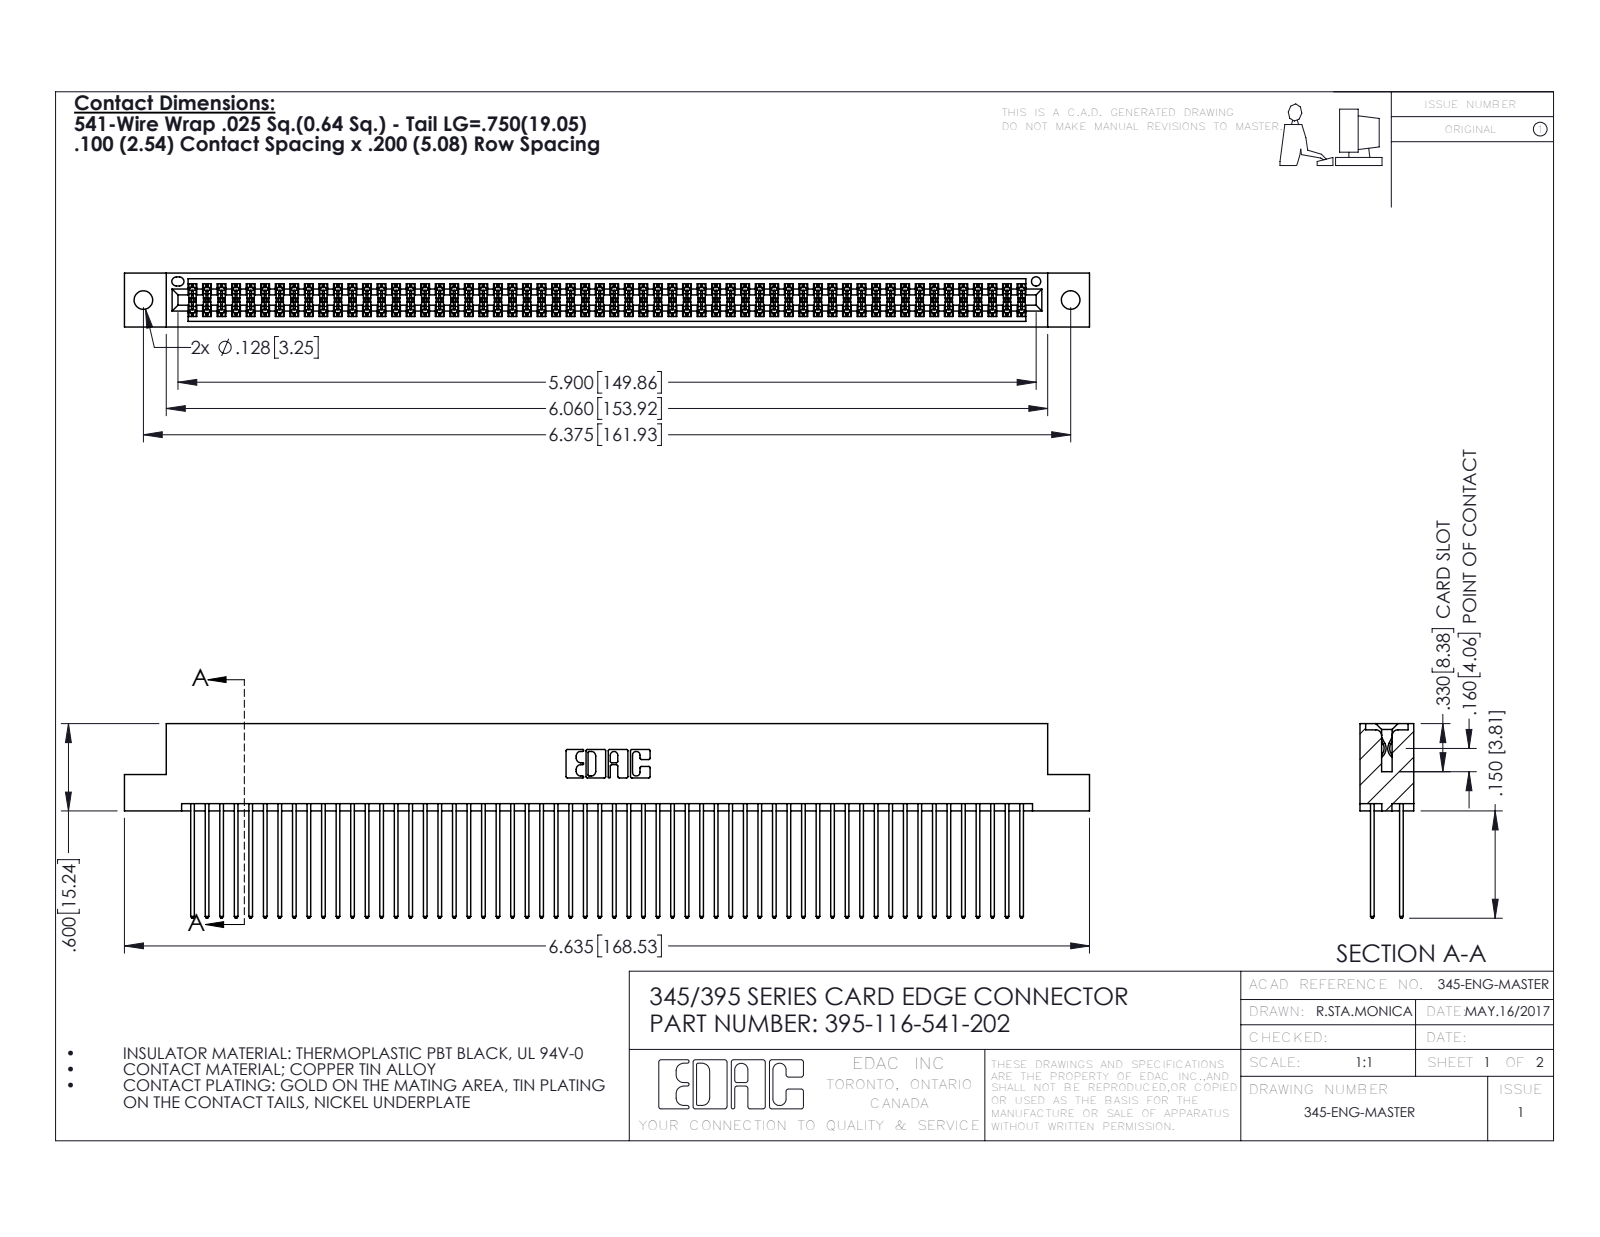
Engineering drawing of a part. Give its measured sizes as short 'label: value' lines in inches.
name: 345-292-001_345-293-141; 395-116-541-202; 345 Part_Flush Mounting Lugs - 0.128 Dia
written by: SolidWorks 2016 (CONFIG_CONTROL_DESIGN)
unit: in
bodies: 117 solids, 5926 faces (3908 planar, 2018 cylindrical, 0 other)
size: 6.635 × 1.337 × 0.37
volume: 1.046 in³; area: 44.2 in²
holes: 2× ⌀0.128, 1× ⌀0.064
rounds: 174× R0.006, 116× R0.01, 22× R0.01, 6× R0.007, 6× R0.031, 3× R0.026, 2× R0.014, 2× R0.019
face distances: 0.298, 0.072, 0.2, 0.098, 0.272, 0.025, 0.225, 0.37, 0.175, 0.149
hole spacings: 0.27, 6.139, 6.375
